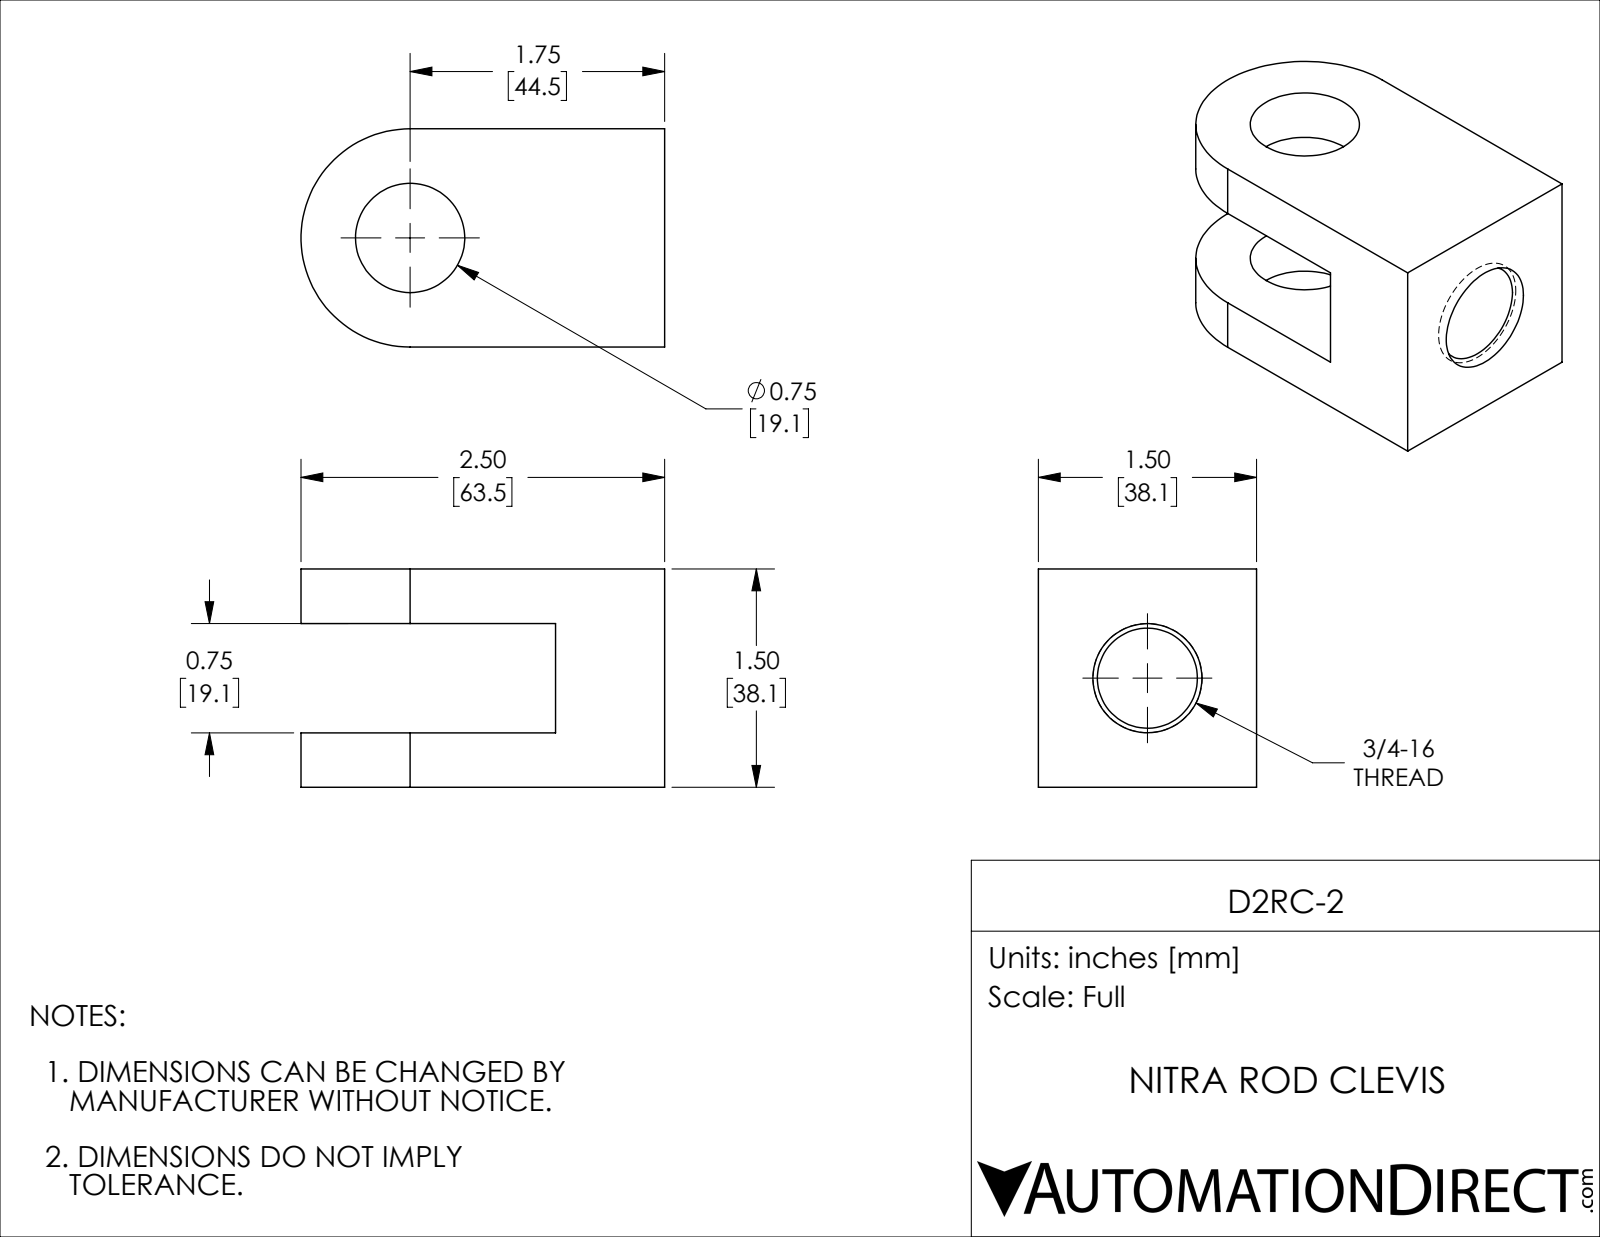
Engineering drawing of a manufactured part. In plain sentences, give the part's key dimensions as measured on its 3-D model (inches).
The part is named "D2RC-2". Its 3-D file was written by "SolidWorks 2019 (CONFIG_CONTROL_DESIGN)". It is 1 solid with 20 faces: 8 planar, 8 cylindrical and 4 other. Overall it measures 2.5 by 1.5 by 1.5 inches. Its volume is 2.855 cubic inches and its surface area 21.44 square inches. Round holes: 1 of diameter 0.687, 1 of diameter 0.751. Partial cylindrical surfaces (rounded edges, fillets, slot ends): 1 of radius 0.75. The main face-to-face distances are 1.5, 0.374, 1.126, 0.752, 0.75.
